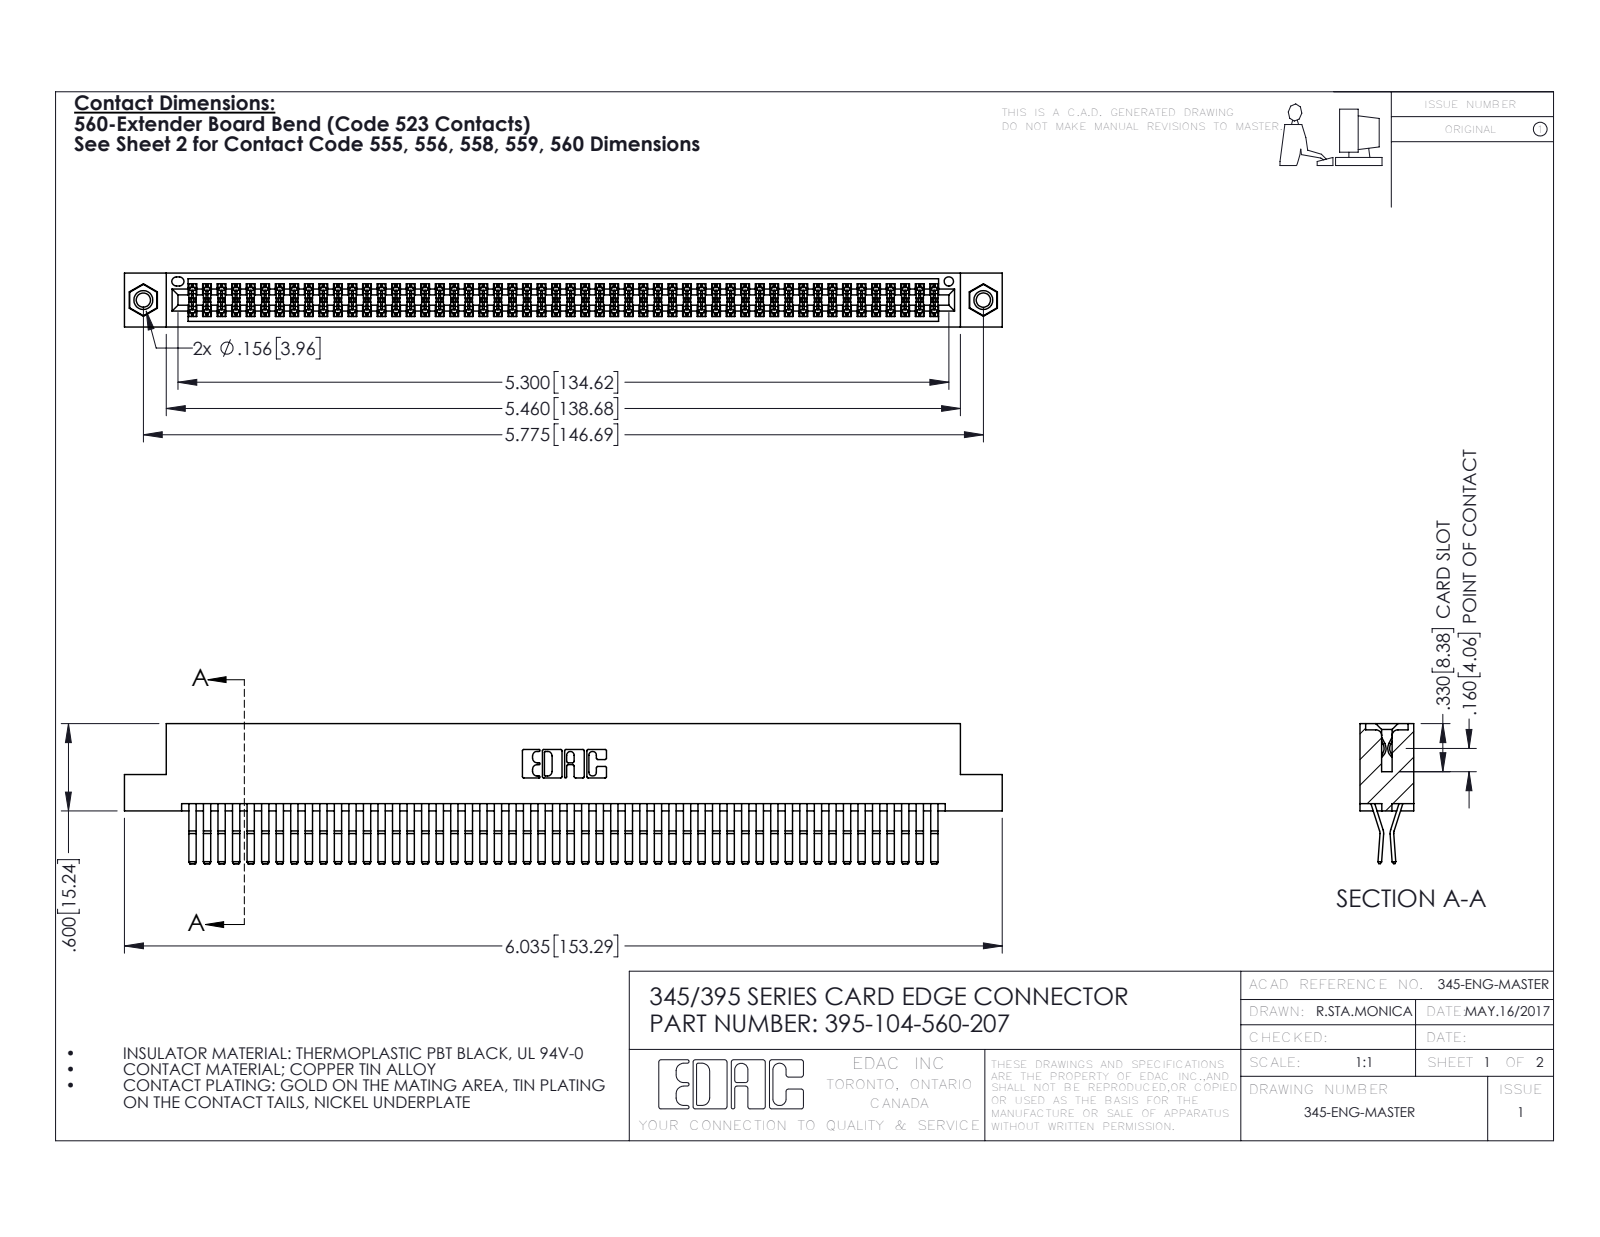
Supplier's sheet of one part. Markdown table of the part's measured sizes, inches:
| quantity | value |
| --- | --- |
| part name | 345-250-001_345-250-005-103; 345 Part_Flush Mounting Lugs - 0.156 Dia-TI; 345-292-001_560 Tail; 395-104-560-207 |
| STEP written by | SolidWorks 2016 (CONFIG_CONTROL_DESIGN) |
| units | inches |
| bodies | 107 solids, 5594 faces (3544 planar, 2034 cylindrical, 16 other) |
| overall size | 6.035 × 0.962 × 0.37 |
| volume | 0.955 in³ |
| surface area | 38.92 in² |
| round holes (diameter × count) | 0.098 × 2, 0.125 × 2, 0.156 × 2, 0.064 × 1 |
| round bosses / shafts (diameter × count) | 0.155 × 2 |
| partial cylindrical surfaces (radius × count) | 0.006 × 156, 0.01 × 22, 0.007 × 6, 0.031 × 6, 0.026 × 3, 0.01 × 2, 0.014 × 2, 0.019 × 2 |
| main face-to-face distances | 0.025, 0.072, 0.298, 0.37, 0.2, 0.098, 0.272, 0.225, 0.175, 0.149 |
| hole center spacings | 0.27, 5.539, 5.775 |
